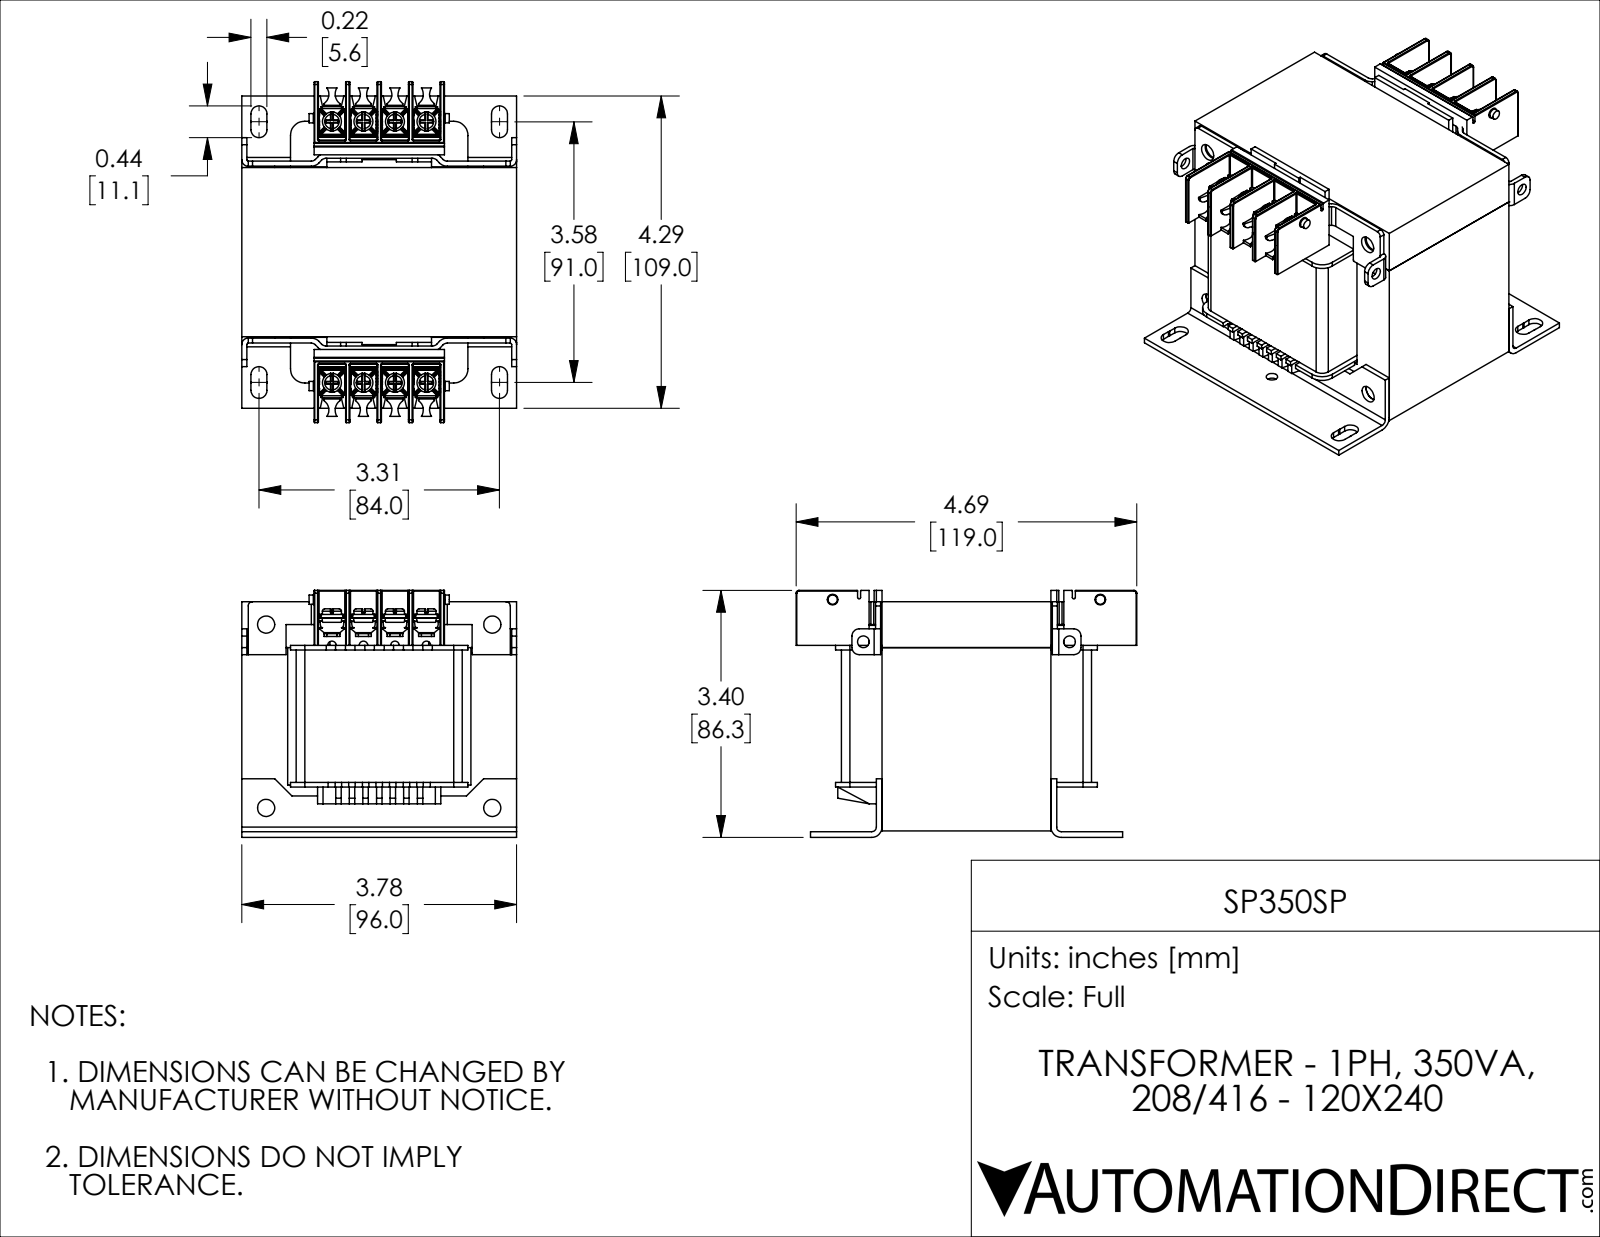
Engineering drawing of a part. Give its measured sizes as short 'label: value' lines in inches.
name: SP350SP
written by: SolidWorks 2018 (AUTOMOTIVE_DESIGN)
unit: in
bodies: 41 solids, 3229 faces (1997 planar, 934 cylindrical, 298 other)
size: 4.685 × 3.78 × 3.396
volume: 33.57 in³; area: 220.2 in²
holes: 10× ⌀0.157, 8× ⌀0.105, 8× ⌀0.138, 4× ⌀0.236, 2× ⌀0.161
bosses: 8× ⌀0.262, 8× ⌀0.24, 8× ⌀0.168, 8× ⌀0.11, 2× ⌀0.128
rounds: 62× R0.01, 52× R0.005, 42× R0.012, 32× R0.029, 16× R0.157, 12× R0.035, 12× R0.065, 10× R0.079
face distances: 0.63, 2.52, 3.15, 2.402, 1.26, 0.079, 2.323, 1.89, 0.748, 3.031
hole spacings: 0.433, 0.866, 3.607, 1.299, 3.581, 3.684, 3.597, 3.617
